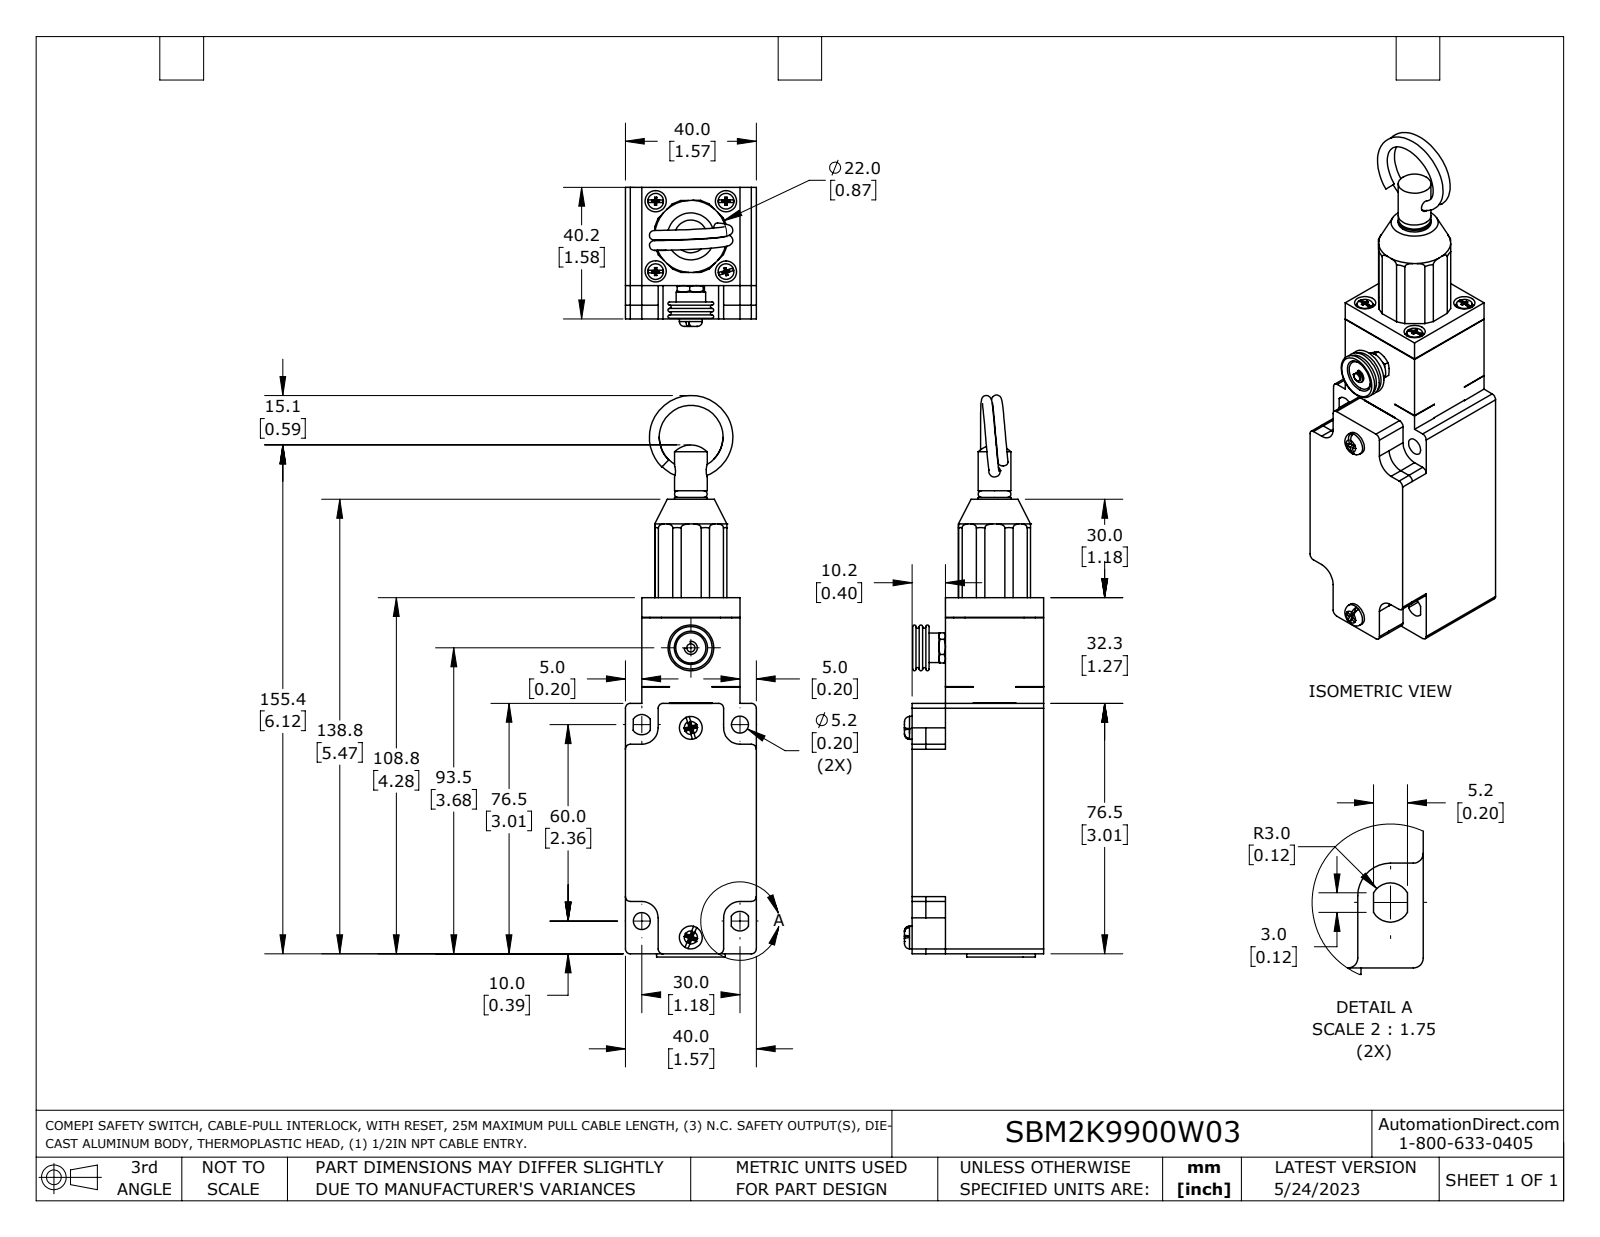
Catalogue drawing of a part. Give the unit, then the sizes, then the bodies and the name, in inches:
Units: inches
Overall size (bounding box): 6.759 × 1.673 × 1.575
Round holes (diameter × count): ⌀0.118 ×4, ⌀0.256 ×4, ⌀0.13 ×2, ⌀0.205 ×2, ⌀0.138 ×1, ⌀0.728 ×1, ⌀0.866 ×1
Round bosses / shafts (diameter × count): ⌀0.189 ×4, ⌀0.276 ×2, ⌀0.827 ×1, ⌀0.394 ×1, ⌀0.354 ×1, ⌀0.248 ×1, ⌀0.098 ×1
Partial cylindrical surfaces — rounded edges, fillets, slot ends (radius × count): R0.059 ×12, R0.197 ×4, R0.039 ×1, R0.079 ×1, R0.117 ×1, R0.119 ×1, R0.122 ×1, R0.123 ×1
Main face-to-face distances: 0.197, 1.575, 1.181, 1.583, 1.378, 0.402, 4.039, 4.047, 3.012, 1.028
Hole centre spacings: 0.846, 0.598, 0.546, 0.657, 1.197, 0.079, 0.592, 0.596
Volume: 9.004 in³ · Surface area: 50.74 in²
Bodies: 3 solids, 353 faces (239 planar, 70 cylindrical, 44 other)
Part name (STEP PRODUCT): SBM2K9900W03_REV1
STEP written by: SolidWorks 2021 (AUTOMOTIVE_DESIGN)
